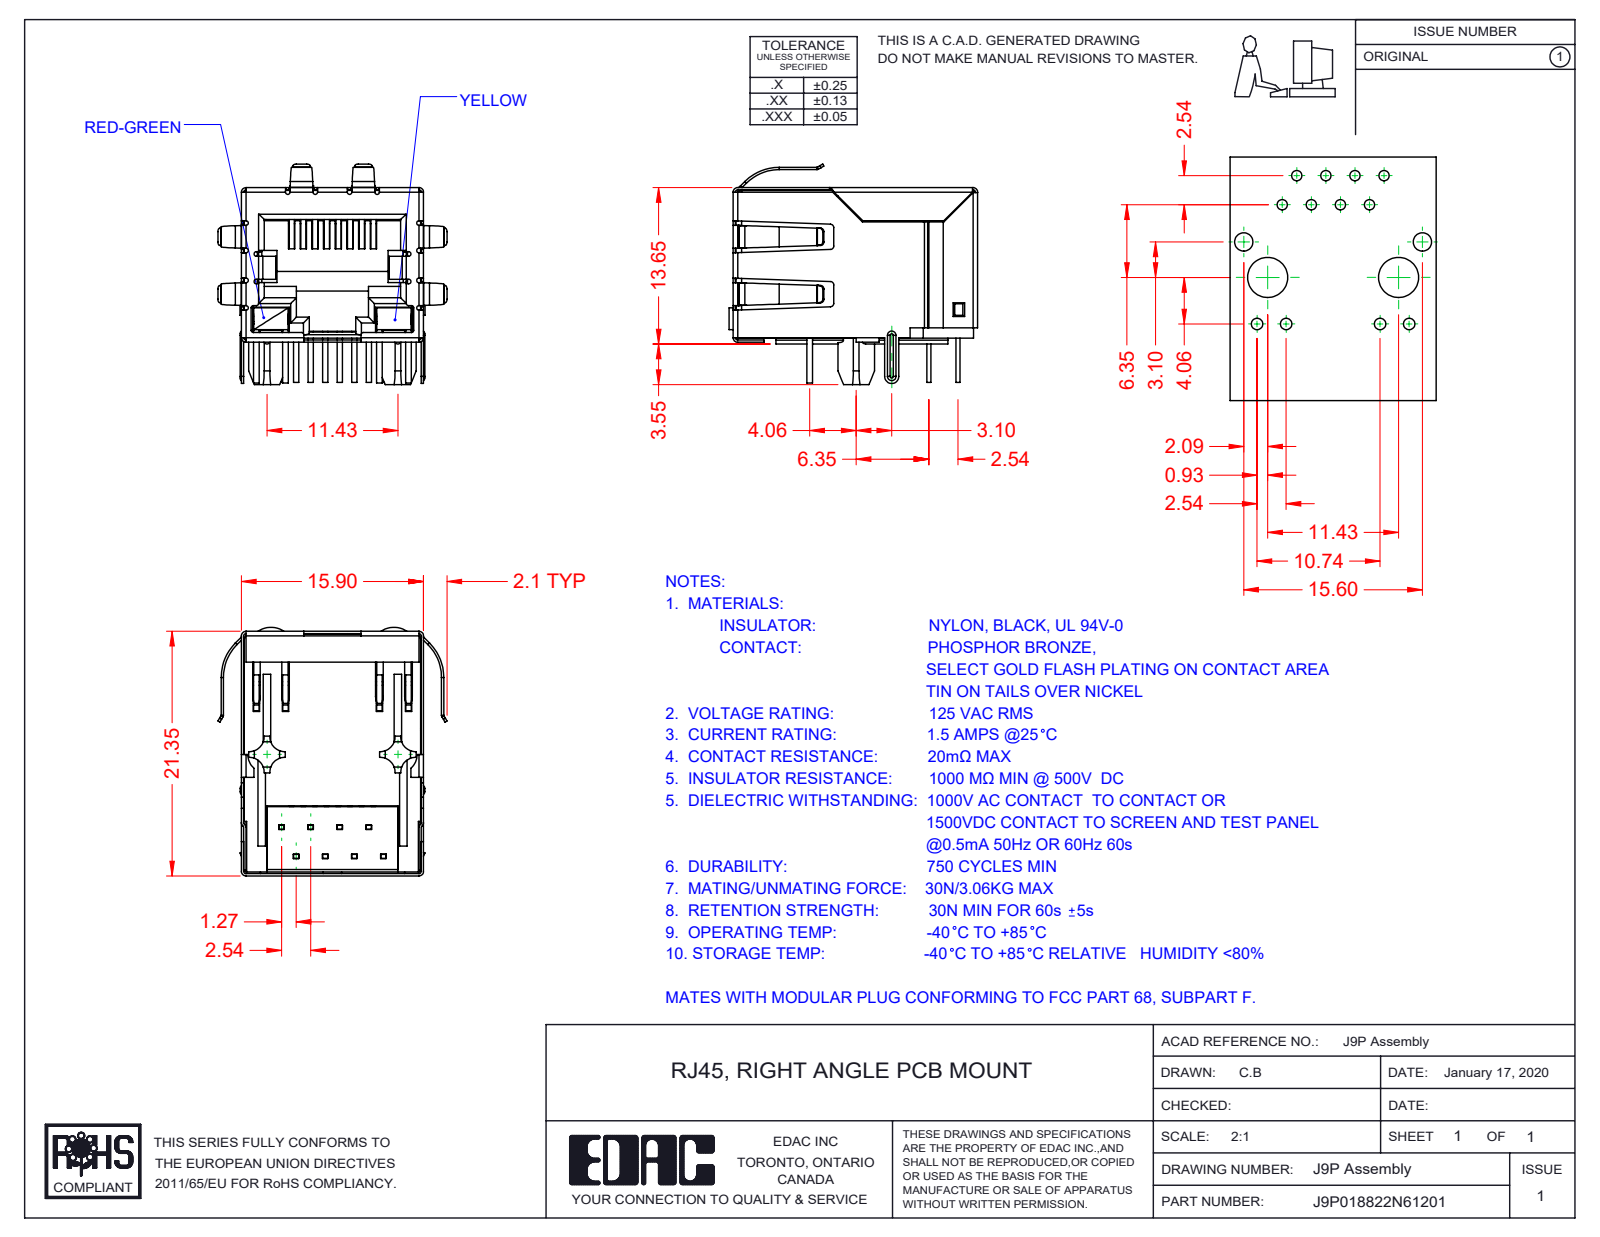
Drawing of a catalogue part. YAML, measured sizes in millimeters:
part_name: "9P-LED Insulator; 9P-LED Assembly; 9P-LED LED RH_1-Yellow; J9P018822N61202 (+4 more)"
step_written_by: "SolidWorks 2016 (CONFIG_CONTROL_DESIGN)"
units: millimeters
bodies: {solids: 13, faces: 1474, planar: 1042, cylindrical: 338, other: 94}
overall_size: [21.7, 20, 19.25]
volume: 2687
surface_area: 7515
partial_cylinders:
  - {radius: 0.2, count: 39}
  - {radius: 0.5, count: 22}
  - {radius: 0.3, count: 20}
  - {radius: 0.4, count: 16}
  - {radius: 1.3, count: 8}
  - {radius: 0.23, count: 5}
  - {radius: 0.11, count: 4}
  - {radius: 0.31, count: 4}
face_to_face_distances: [15.45, 15.7, 15.65, 0.35, 0.54, 15.5, 12.36, 0.6, 1.4, 0.59]
